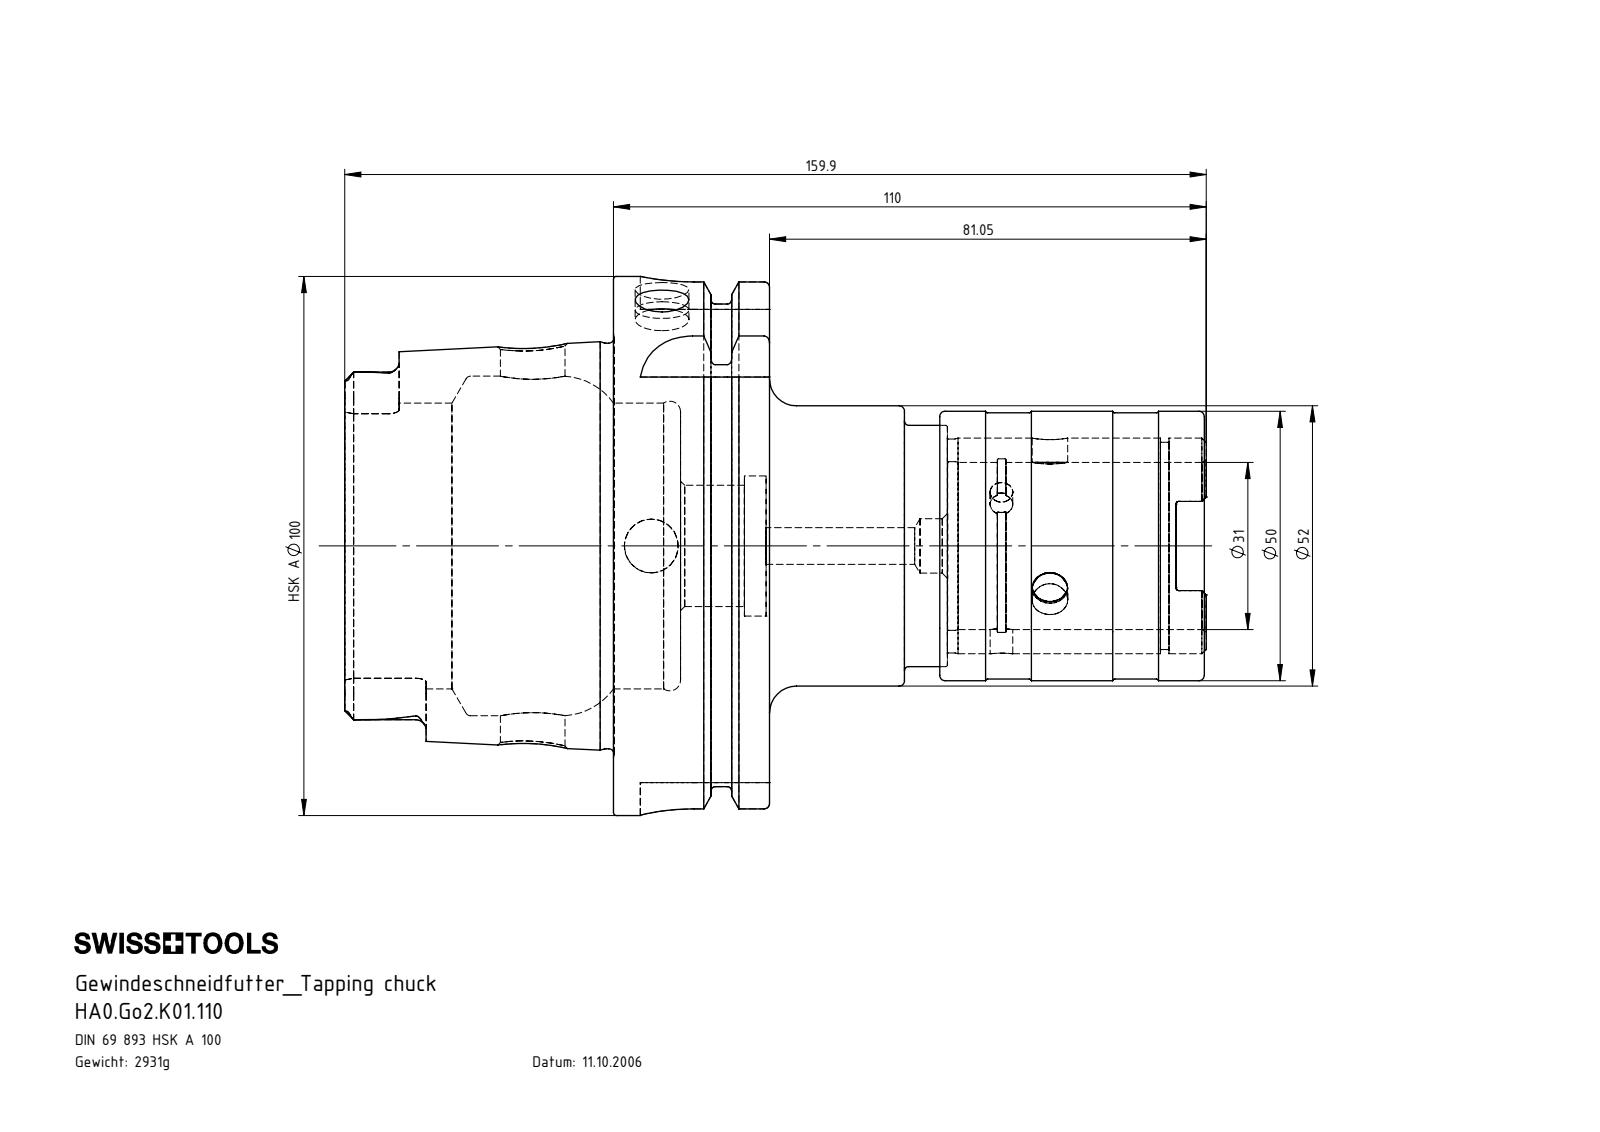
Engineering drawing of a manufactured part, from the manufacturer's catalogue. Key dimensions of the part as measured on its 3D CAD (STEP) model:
Part name (STEP PRODUCT): HA0.Go2.K01.110; Einbausatz Go2_gespannt; Kugel Go2; Hülse Go2 (+6 more)
STEP written by: SolidWorks 2011 (AUTOMOTIVE_DESIGN)
Units: millimetres
Bodies: 10 solids, 378 faces (84 planar, 122 cylindrical, 172 other)
Overall size (bounding box): 159.9 × 100 × 100
Volume: 373 342 mm³ · Surface area: 89 624 mm²
Round holes (diameter × count): ⌀4.2 ×3, ⌀6.6 ×3, ⌀10 ×3, ⌀2.5 ×1, ⌀6.8 ×1, ⌀10.1 ×1, ⌀12 ×1, ⌀22.5 ×1, ⌀26 ×1, ⌀31 ×1, ⌀31.3 ×1, ⌀32.35 ×1
Round bosses / shafts (diameter × count): ⌀100 ×1, ⌀91.95 ×1, ⌀75.26 ×1, ⌀52 ×1, ⌀50 ×1, ⌀49.4 ×1, ⌀44.75 ×1, ⌀40 ×1
Partial cylindrical surfaces — rounded edges, fillets, slot ends (radius × count): R1.9 ×6, R4.88 ×4, R10 ×4, R3.1 ×3, R0.5 ×2
Main face-to-face distances: 28.95, 12.45, 16.5, 0.65, 33.7, 49.9, 62.35, 78.85, 47.6, 124.55
Hole centre spacings: 9, 87, 96
